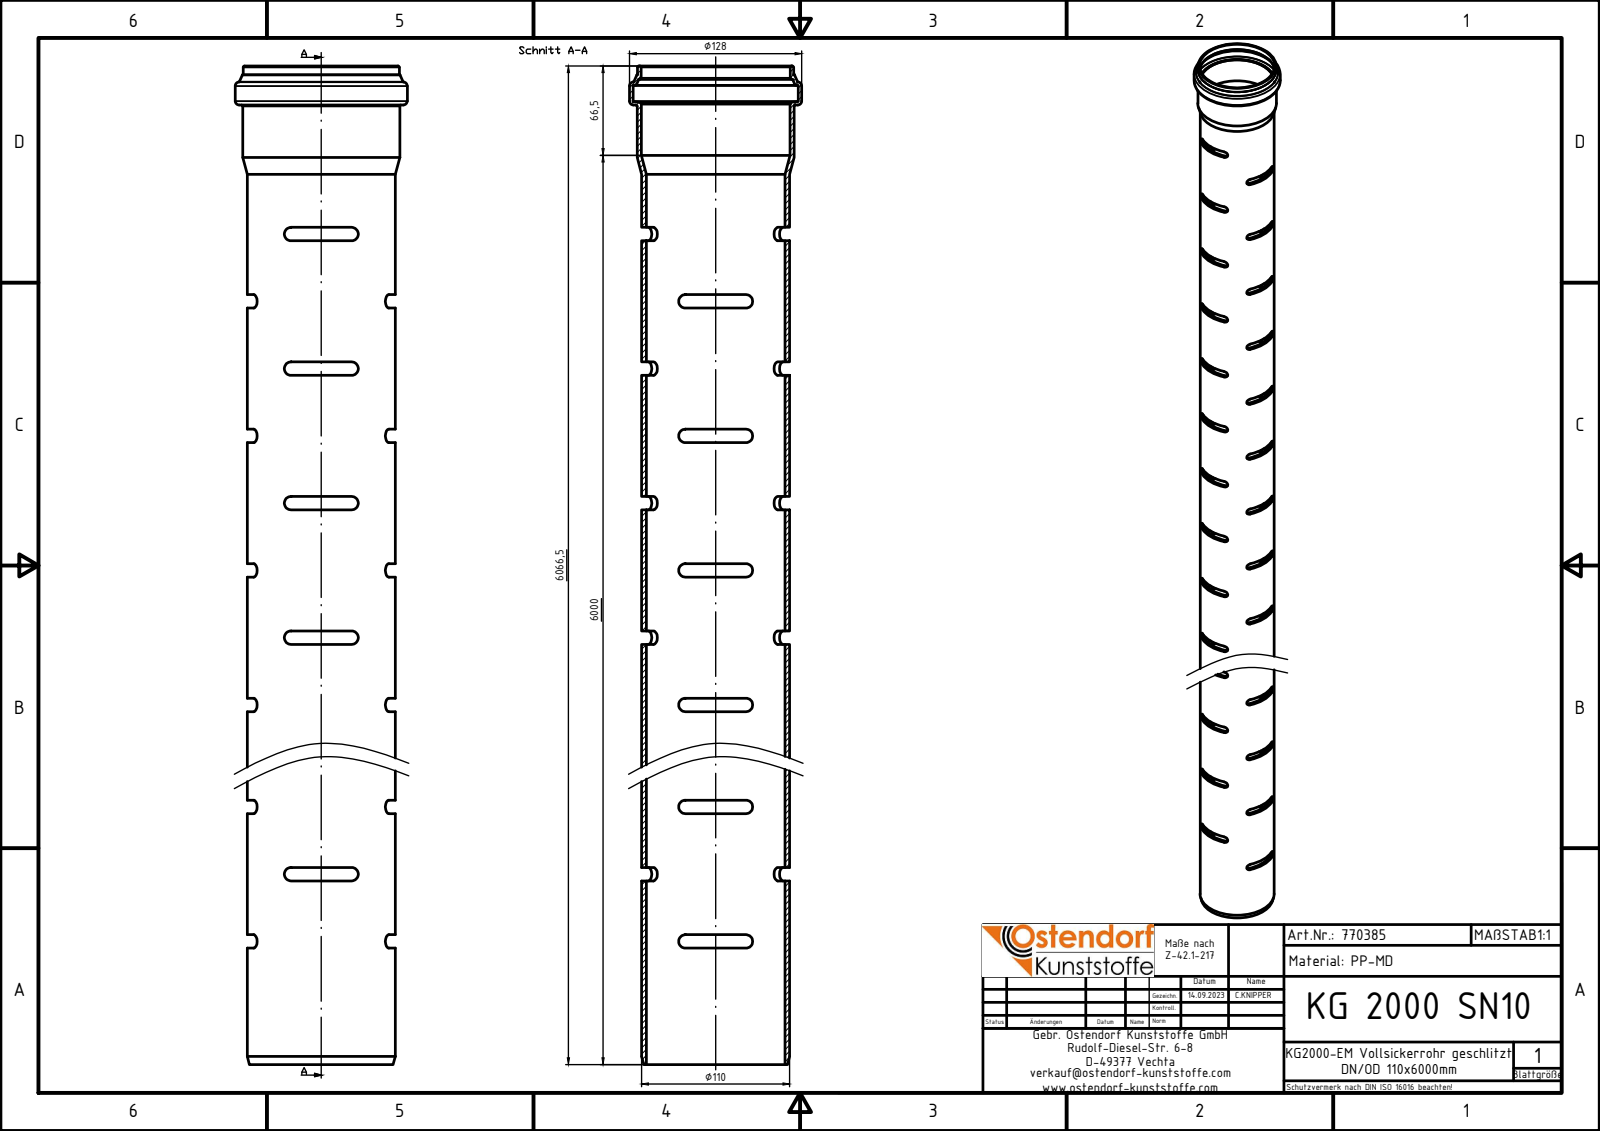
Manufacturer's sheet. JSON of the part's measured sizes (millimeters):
{"part_name": "770385z", "step_written_by": "Autodesk Inventor 2024 (AUTOMOTIVE_DESIGN)", "units": "millimeters", "bodies": {"solids": 1, "faces": 980, "planar": 477, "cylindrical": 481, "other": 22}, "overall_size": [6066.5, 128, 128], "volume_mm3": 6682000, "surface_area_mm2": 3916000, "round_holes": [[102.96, 1], [110.5, 1], [110.9, 1], [122.8, 1]], "round_bosses_or_shafts": [[128, 1], [116.7, 1], [116.1, 1], [110, 1]], "partial_cylinders_radius": [[5, 236]], "face_to_face_distances": [100, 200, 300, 400, 500, 600, 700, 800, 900, 1000]}
